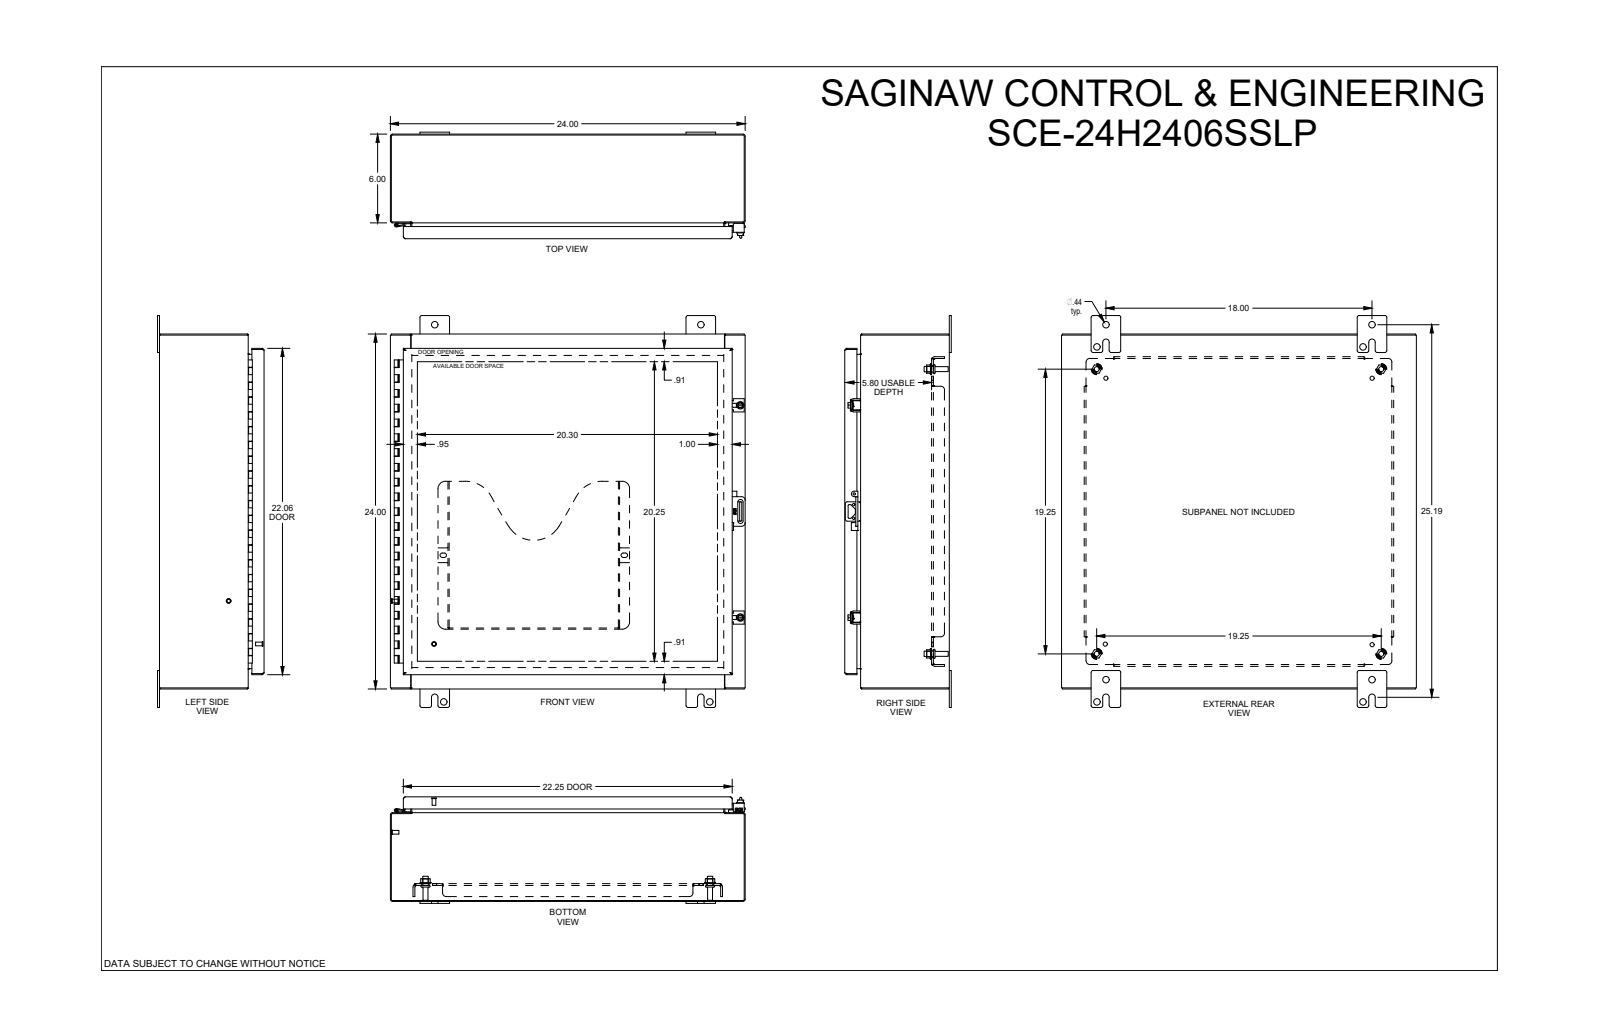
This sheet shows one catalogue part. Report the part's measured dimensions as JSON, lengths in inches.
{"part_name": "SCE-24H2406SSLP", "step_written_by": "SolidWorks 2019 (CONFIG_CONTROL_DESIGN)", "units": "inches", "bodies": {"solids": 0, "faces": 3192, "planar": 1285, "cylindrical": 670, "other": 1237}, "overall_size": [26.5, 24, 7.208], "round_holes": [[0.437, 8], [0.25, 5], [0.19, 4], [0.193, 4], [0.281, 4], [0.367, 4], [0.5, 4], [0.16, 2], [0.203, 2], [0.13, 1], [0.132, 1]], "round_bosses_or_shafts": [[0.248, 7], [0.563, 5], [0.366, 4], [0.332, 4], [0.256, 4], [0.188, 4], [0.25, 3], [0.507, 2]], "partial_cylinders_radius": [[0.01, 114], [0.015, 36], [0.029, 30], [0.03, 27], [0.125, 27], [0.06, 25], [0.04, 22], [0.07, 14]], "face_to_face_distances": [0.075, 23.925, 6.998, 6.923, 1.2, 5.873, 0.075, 7.073, 6.998, 5.923], "hole_center_spacings": [18.641, 0.875, 18, 19.25, 6.5, 26.348, 0.515, 1.439]}
